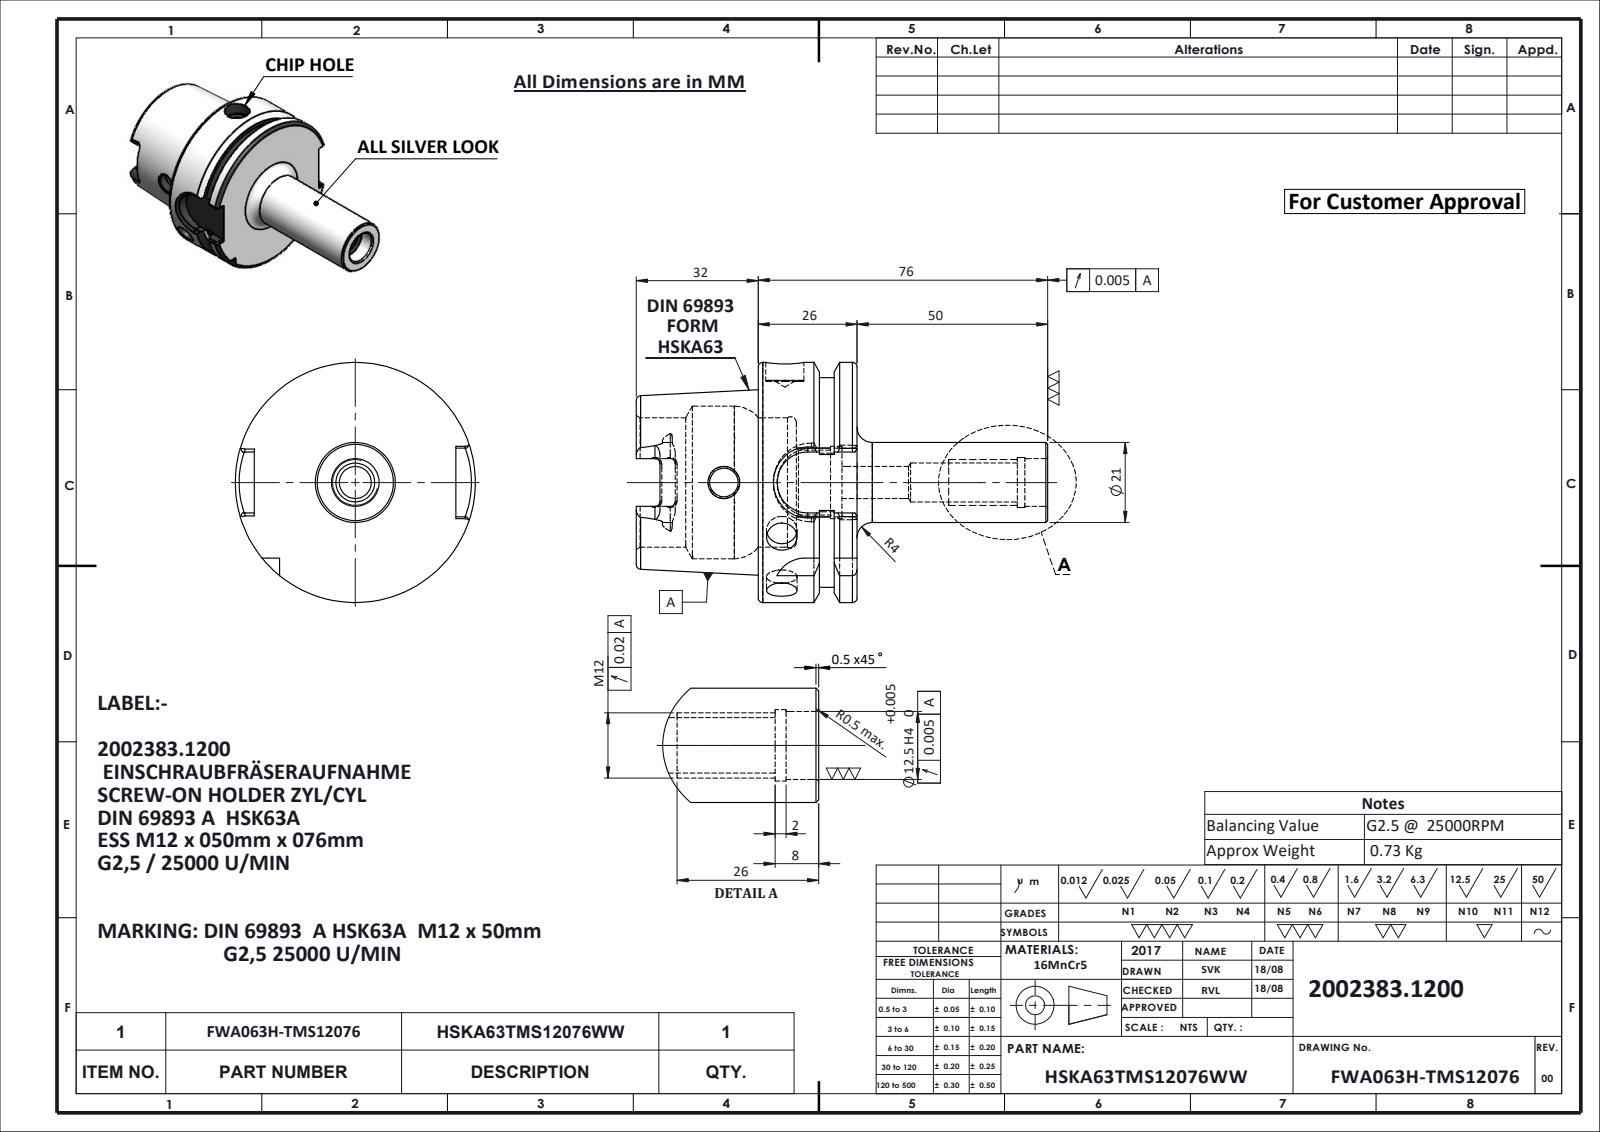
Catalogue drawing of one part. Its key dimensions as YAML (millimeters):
part_name: "HSKA63TMS12076WW; FWA063H-TMS12076"
step_written_by: "SolidWorks 2024 (CONFIG_CONTROL_DESIGN)"
units: millimeters
bodies: {solids: 1, faces: 168, planar: 51, cylindrical: 53, other: 64}
overall_size: [108, 63, 63]
volume: 94302
surface_area: 27106
round_holes:
  - {diameter: 8, count: 2}
  - {diameter: 7.5, count: 1}
  - {diameter: 8.4, count: 1}
  - {diameter: 10, count: 1}
  - {diameter: 10.2, count: 1}
  - {diameter: 12.5, count: 1}
  - {diameter: 13.1, count: 1}
  - {diameter: 17, count: 1}
  - {diameter: 19, count: 1}
  - {diameter: 34, count: 1}
  - {diameter: 40, count: 1}
round_bosses_or_shafts:
  - {diameter: 63, count: 1}
  - {diameter: 55, count: 1}
  - {diameter: 21, count: 1}
partial_cylinders:
  - {radius: 1.3, count: 6}
  - {radius: 2.88, count: 4}
  - {radius: 8, count: 2}
  - {radius: 9, count: 1}
face_to_face_distances: [25.95, 10, 15.95, 54, 32, 42, 57.95, 52.9, 22, 12]
